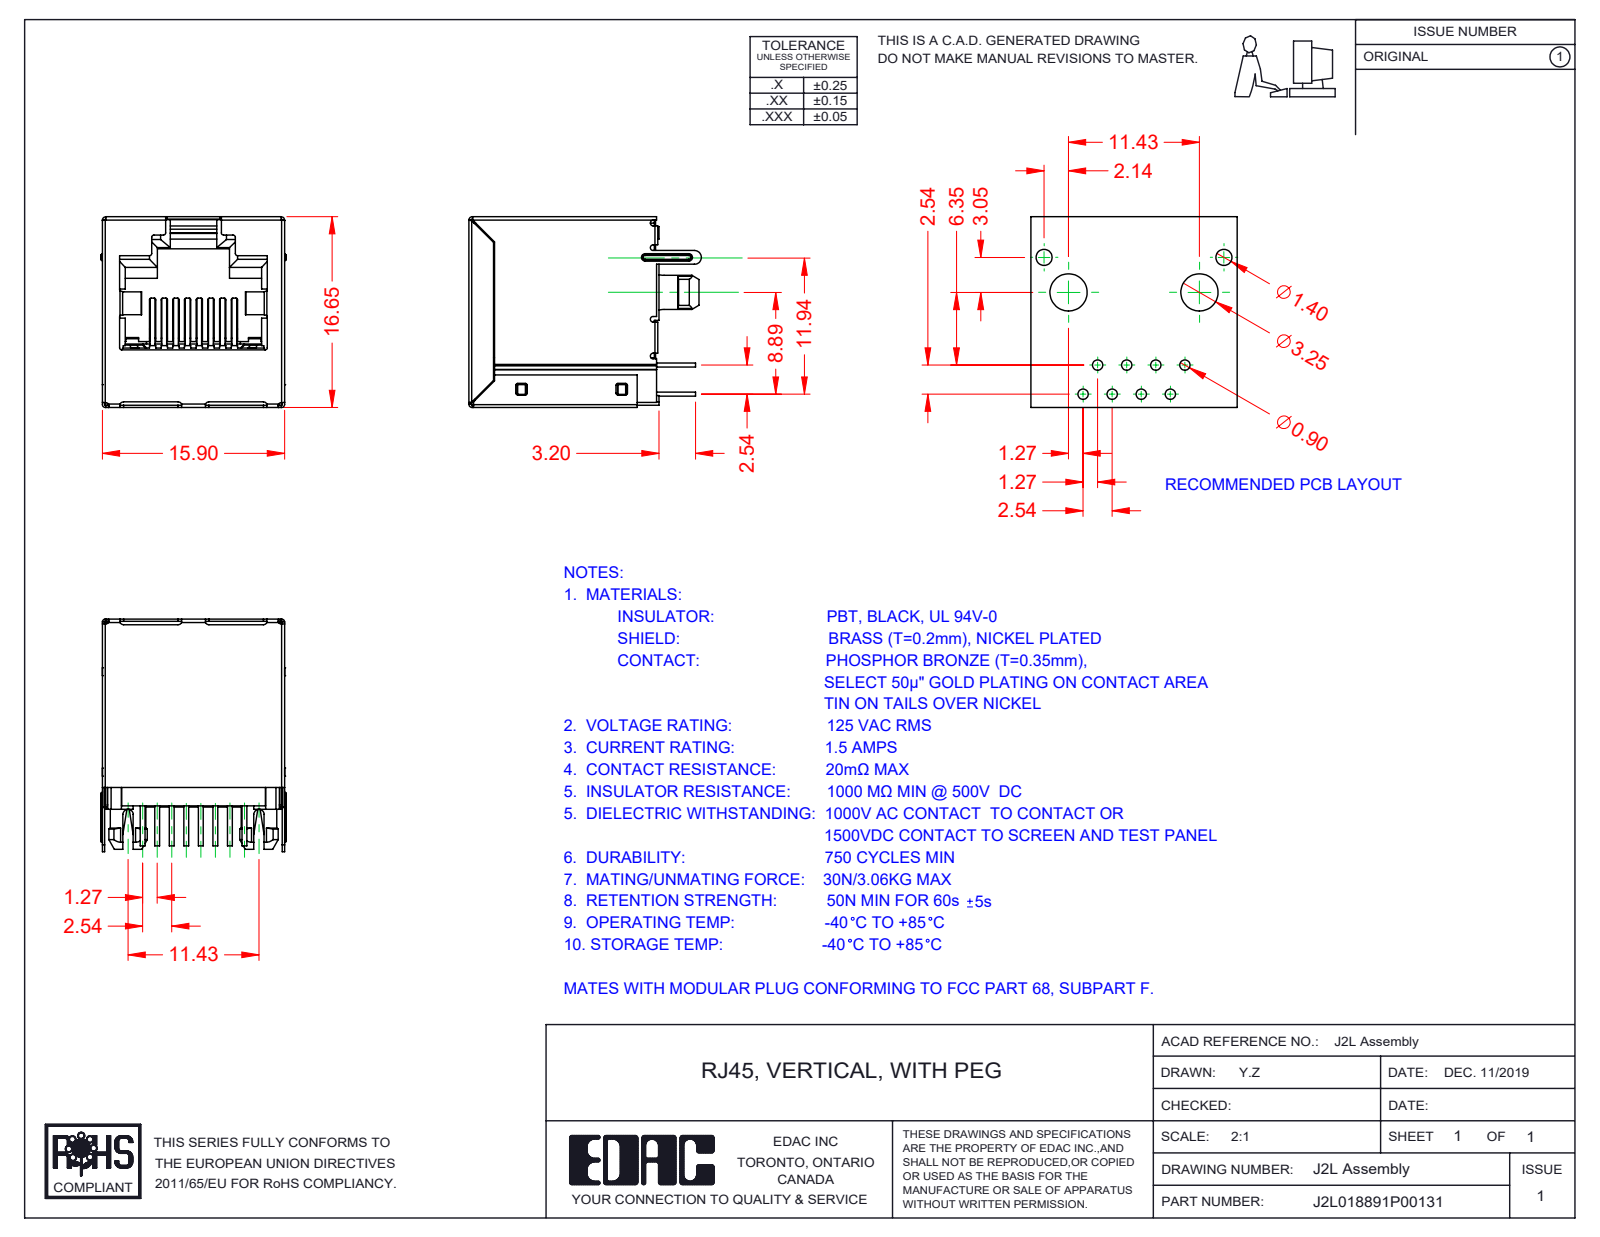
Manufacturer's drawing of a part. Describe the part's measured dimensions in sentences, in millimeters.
The part is named "RJ2L018891P00131; 2L Shield; 2L Contact Lock; 2L Contacts (+1 more)". Its 3-D file was written by "SolidWorks 2016 (CONFIG_CONTROL_DESIGN)". It is 11 solids with 1125 faces: 778 planar, 284 cylindrical and 63 other. Overall it measures 20.3 by 16.65 by 16.2 millimeters. Its volume is 2 717 cubic millimeters and its surface area 6 473 square millimeters. Round bosses or shafts: 2 of diameter 3.1, 2 of diameter 1.1. Partial cylindrical surfaces (rounded edges, fillets, slot ends): 64 of radius 0.15, 20 of radius 0.25, 16 of radius 0.2, 14 of radius 0.3, 9 of radius 0.35, 8 of radius 0.1, 4 of radius 0.28, 3 of radius 0.5. The main face-to-face distances are 15.45, 15.7, 16.45, 16.2, 16.4, 15.65, 16.25, 15.9, 15.5, 1.2.
